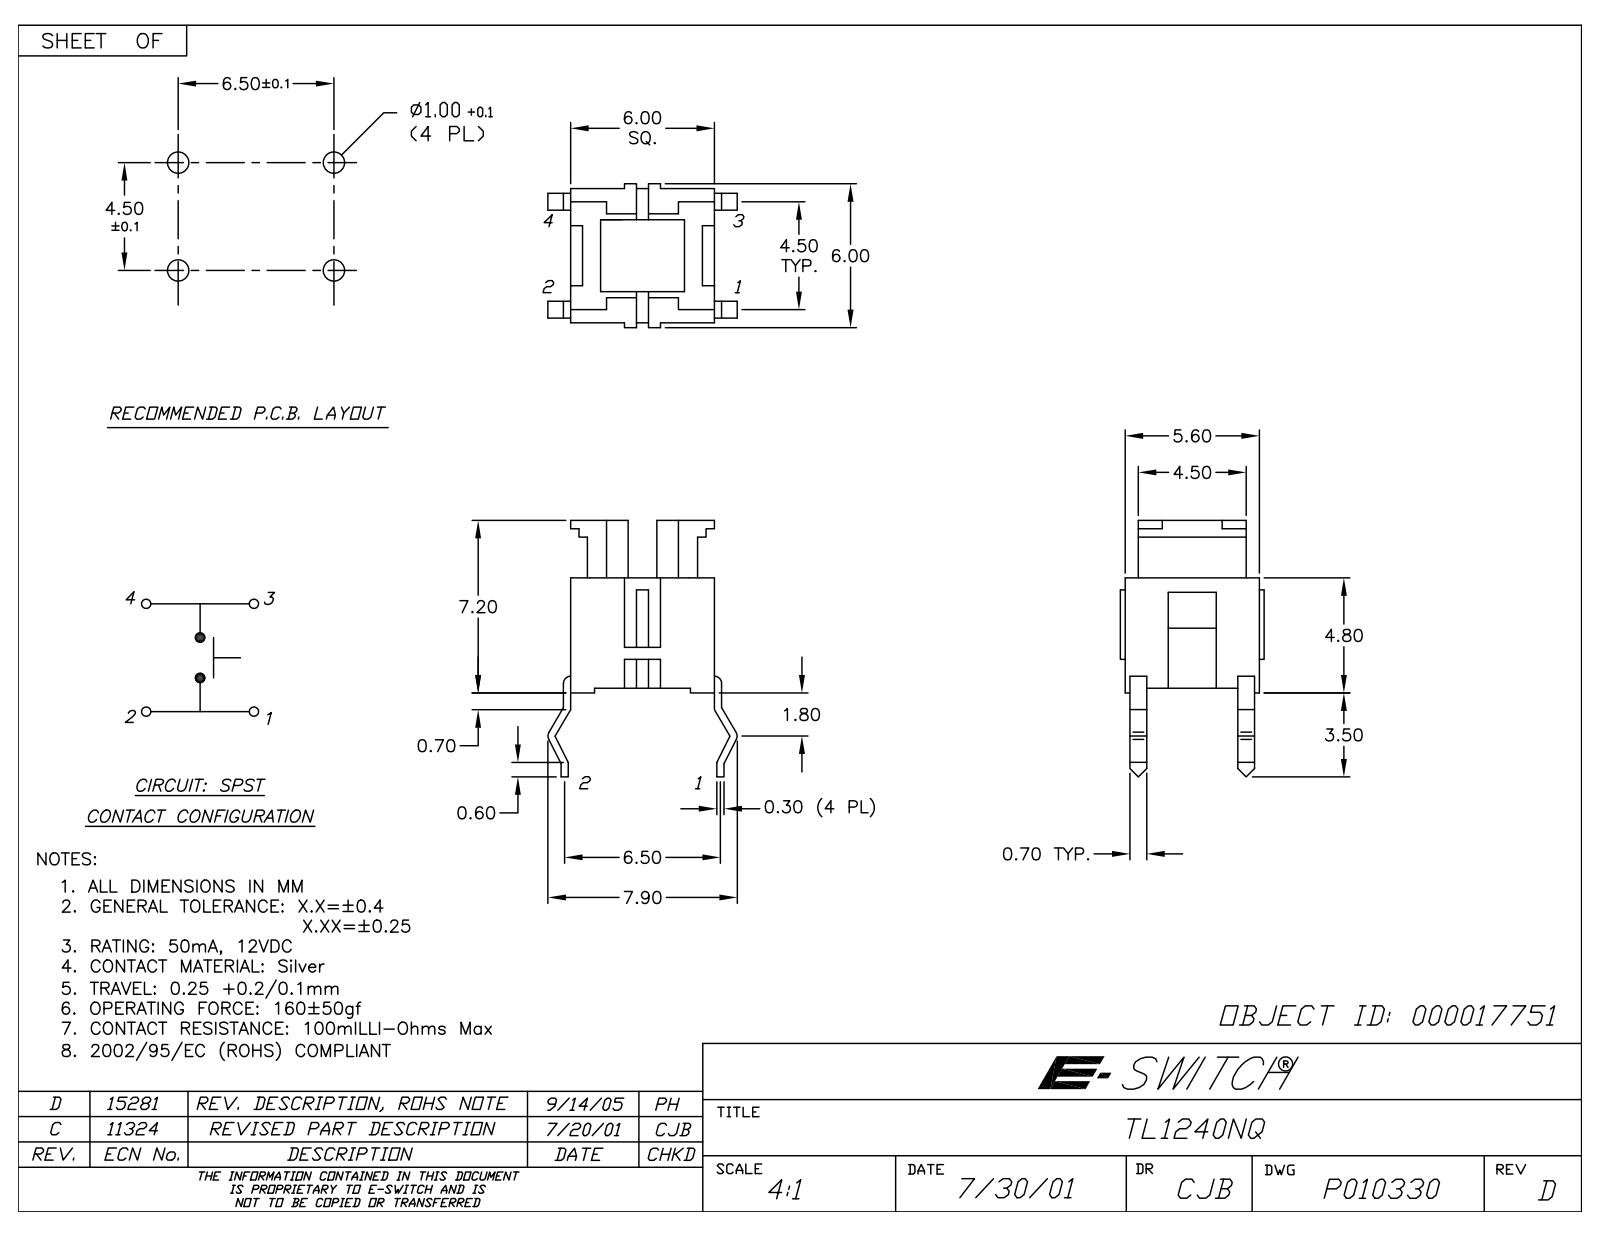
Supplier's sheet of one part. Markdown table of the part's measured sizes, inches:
| quantity | value |
| --- | --- |
| part name | P:\\\\E-Switch Secure\\\\3D_MODELS_STP_FORMAT\\\\TL1240NQ.stp |
| STEP written by | ACIS (CONFIG_CONTROL_DESIGN) |
| units | inches |
| bodies | 1 solid, 251 faces (216 planar, 34 cylindrical, 1 other) |
| overall size | 0.421 × 0.311 × 0.26 |
| volume | 0.008 in³ |
| surface area | 0.795 in² |
| partial cylindrical surfaces (radius × count) | 0.004 × 6, 0.016 × 6, 0.014 × 2, 0.028 × 1 |
| main face-to-face distances | 0.028, 0.209, 0.03, 0.177, 0.02, 0.179, 0.181, 0.207, 0.161, 0.236 |
